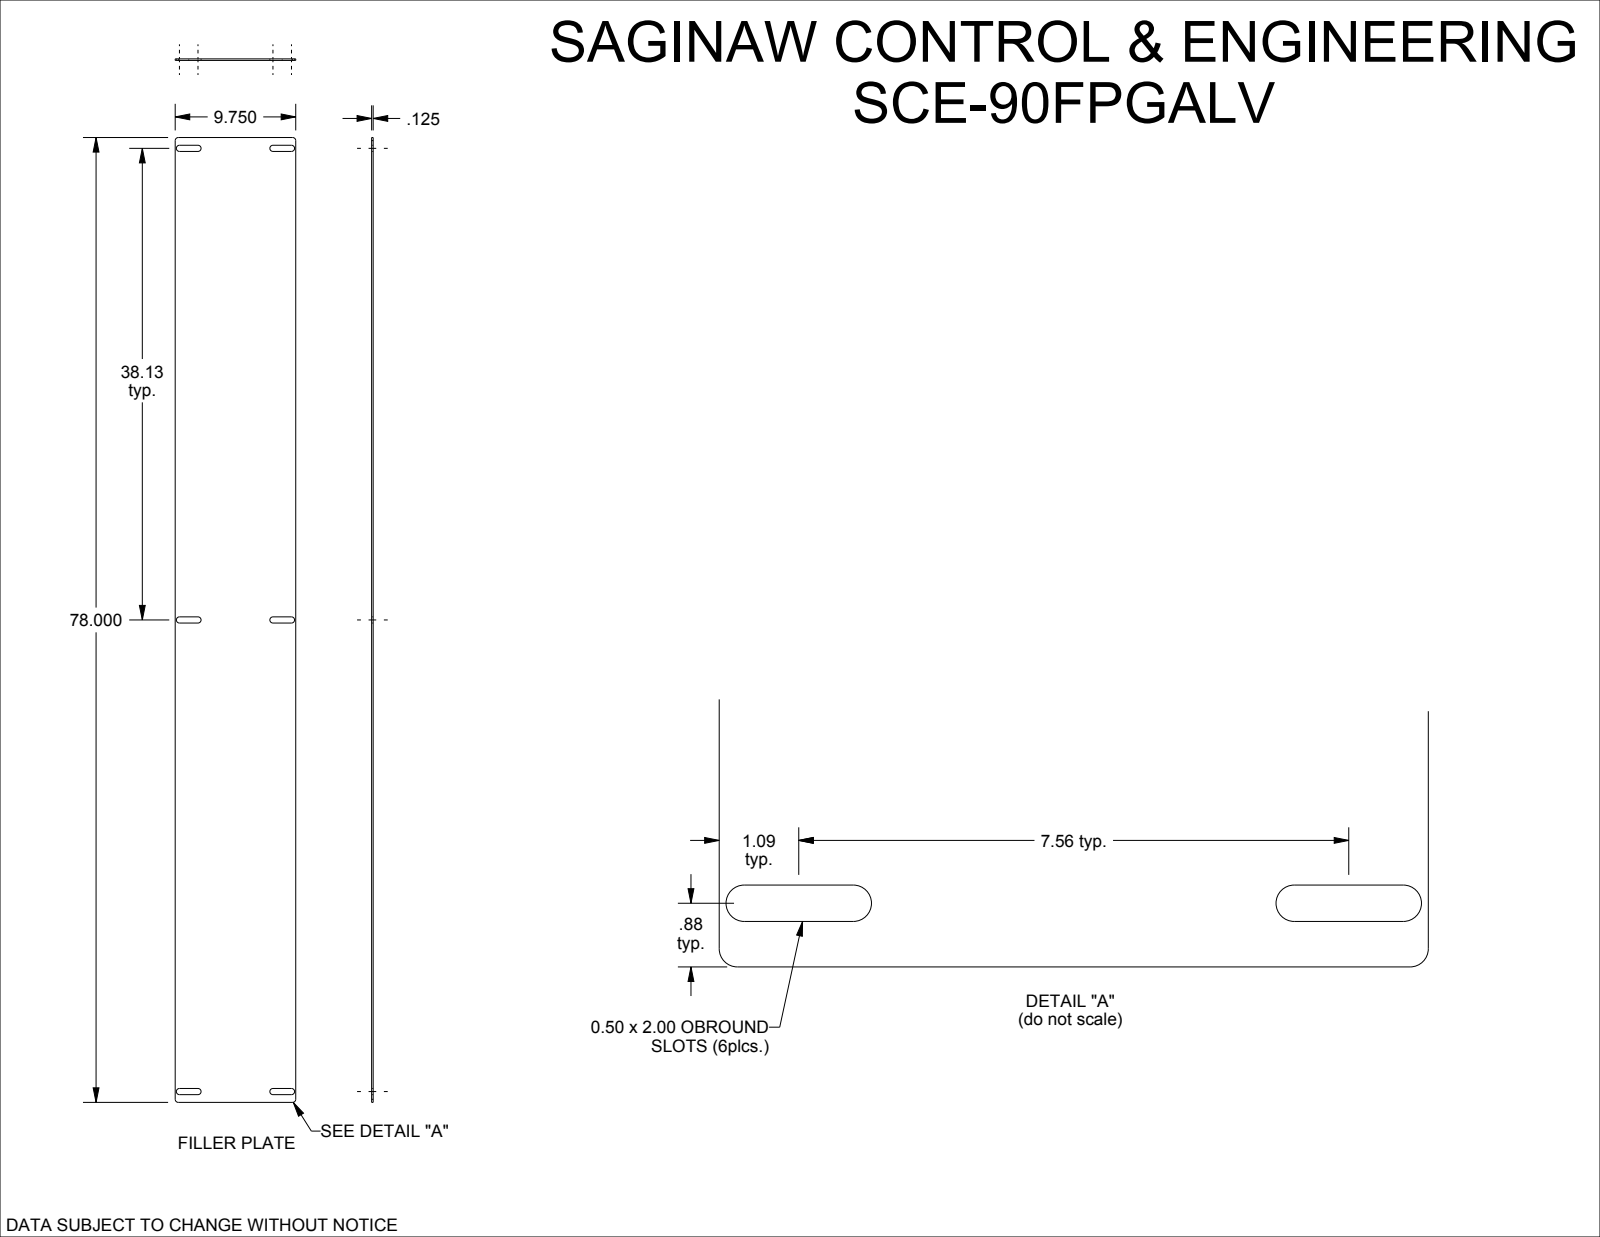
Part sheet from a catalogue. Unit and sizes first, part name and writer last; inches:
Units: inches
Overall size (bounding box): 77.688 × 9.75 × 0.125
Partial cylindrical surfaces — rounded edges, fillets, slot ends (radius × count): R0.25 ×16
Main face-to-face distances: 0.125, 9.75, 38.125, 77.687, 0.5, 38.594, 39.094, 0.969, 76.719, 0.469
Volume: 93.97 in³ · Surface area: 1 529 in²
Bodies: 1 solid, 46 faces (30 planar, 16 cylindrical, 0 other)
Part name (STEP PRODUCT): SCE-90FPGALV
STEP written by: SolidWorks 2023 (AUTOMOTIVE_DESIGN)
